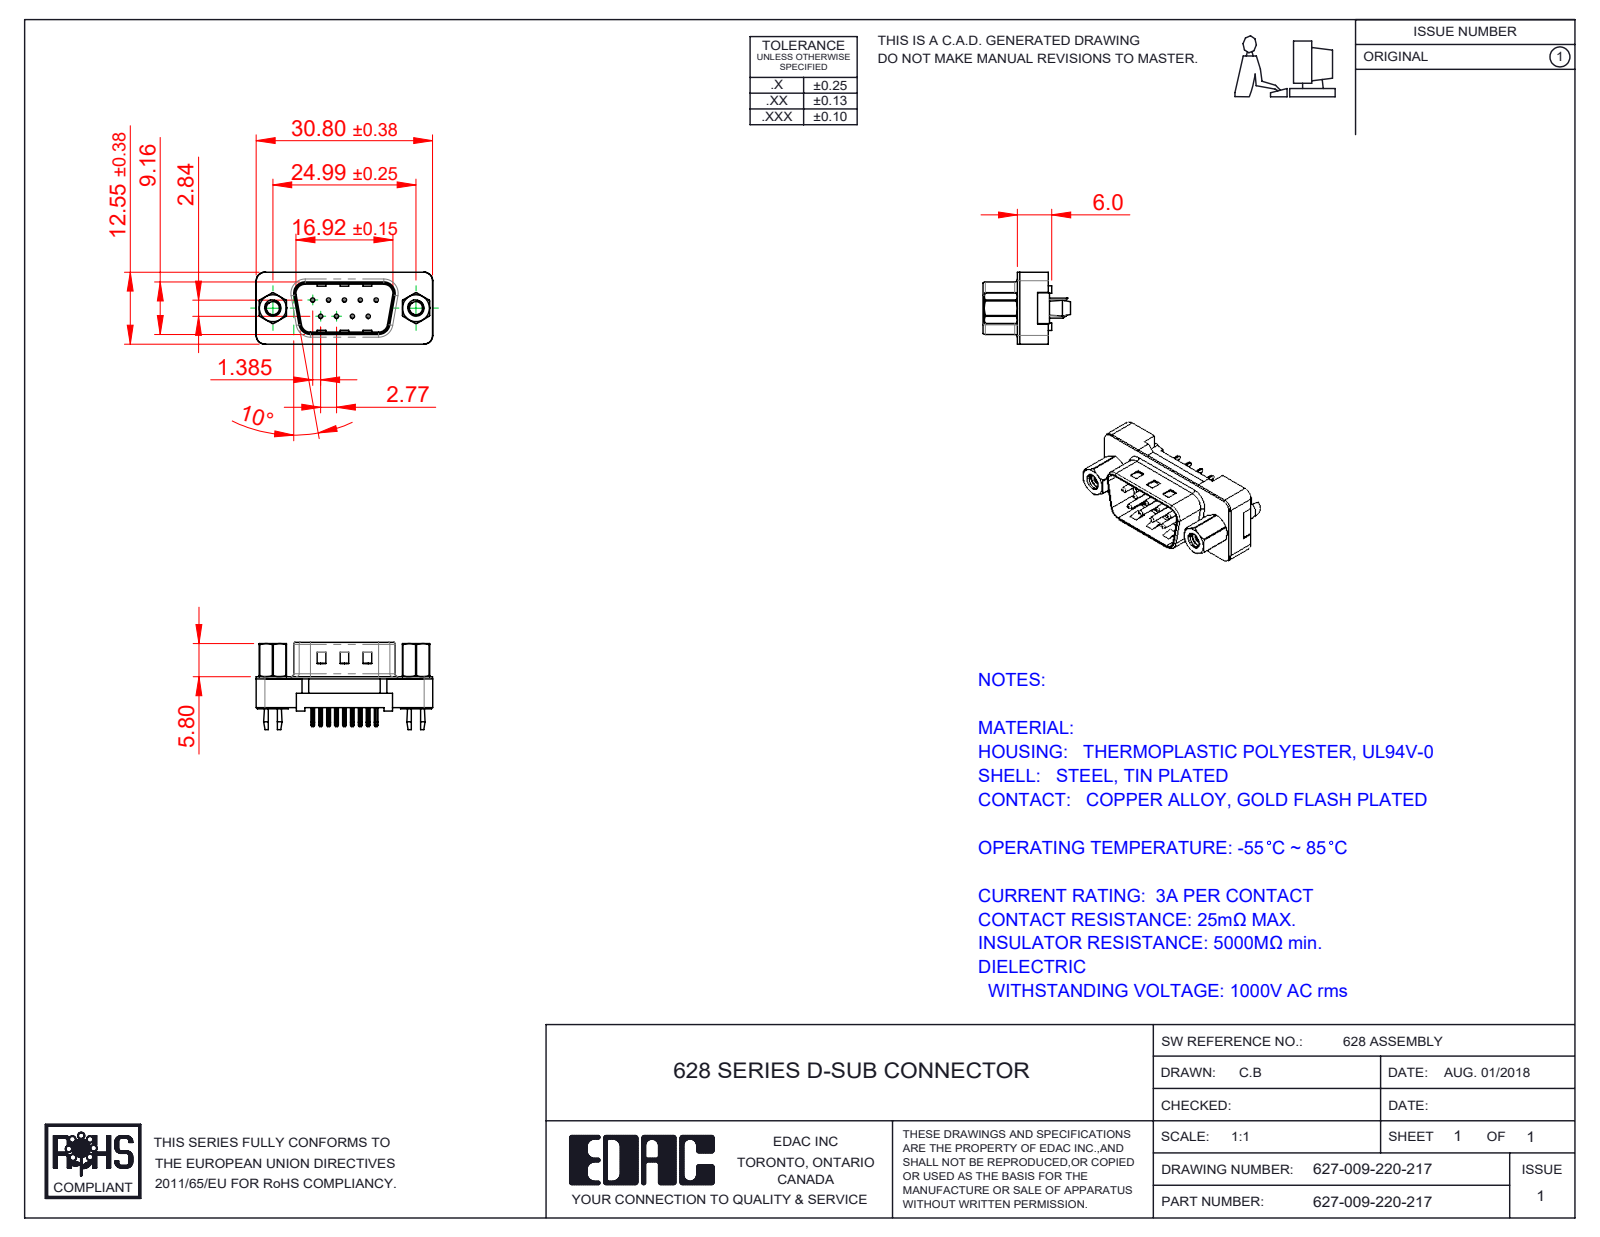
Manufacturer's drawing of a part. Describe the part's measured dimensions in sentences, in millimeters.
The part is named "627-009-220-217; 627 4-40 Hex Standoff; 627 Plastic Body Housing_09 Contacts; 627 PB 4-40 Threaded Rivet with Boardlock (+3 more)". Its 3-D file was written by "SolidWorks 2020 (CONFIG_CONTROL_DESIGN)". It is 15 solids with 925 faces: 513 planar, 306 cylindrical and 106 other. Overall it measures 30.81 by 15.25 by 12.55 millimeters. Its volume is 1 890 cubic millimeters and its surface area 3 916 square millimeters. Round holes: 9 of diameter 0.35, 9 of diameter 0.85, 2 of diameter 2.26, 2 of diameter 2.29, 2 of diameter 4, 2 of diameter 4.8, 2 of diameter 5. Round bosses or shafts: 9 of diameter 0.75, 2 of diameter 4.9, 2 of diameter 2.79. Partial cylindrical surfaces (rounded edges, fillets, slot ends): 18 of radius 0.25, 9 of radius 0.12, 8 of radius 0.5, 7 of radius 1.5, 4 of radius 0.9, 4 of radius 1.6, 4 of radius 2, 2 of radius 0.4. The main face-to-face distances are 0.4, 2.5, 5.4, 5, 1.58, 2.1, 3.5, 2.9, 8.76, 1.9. The hole center spacings are 3.16, 2.77, 5.04, 5.54, 7.49, 5.03, 7.09, 8.31.
